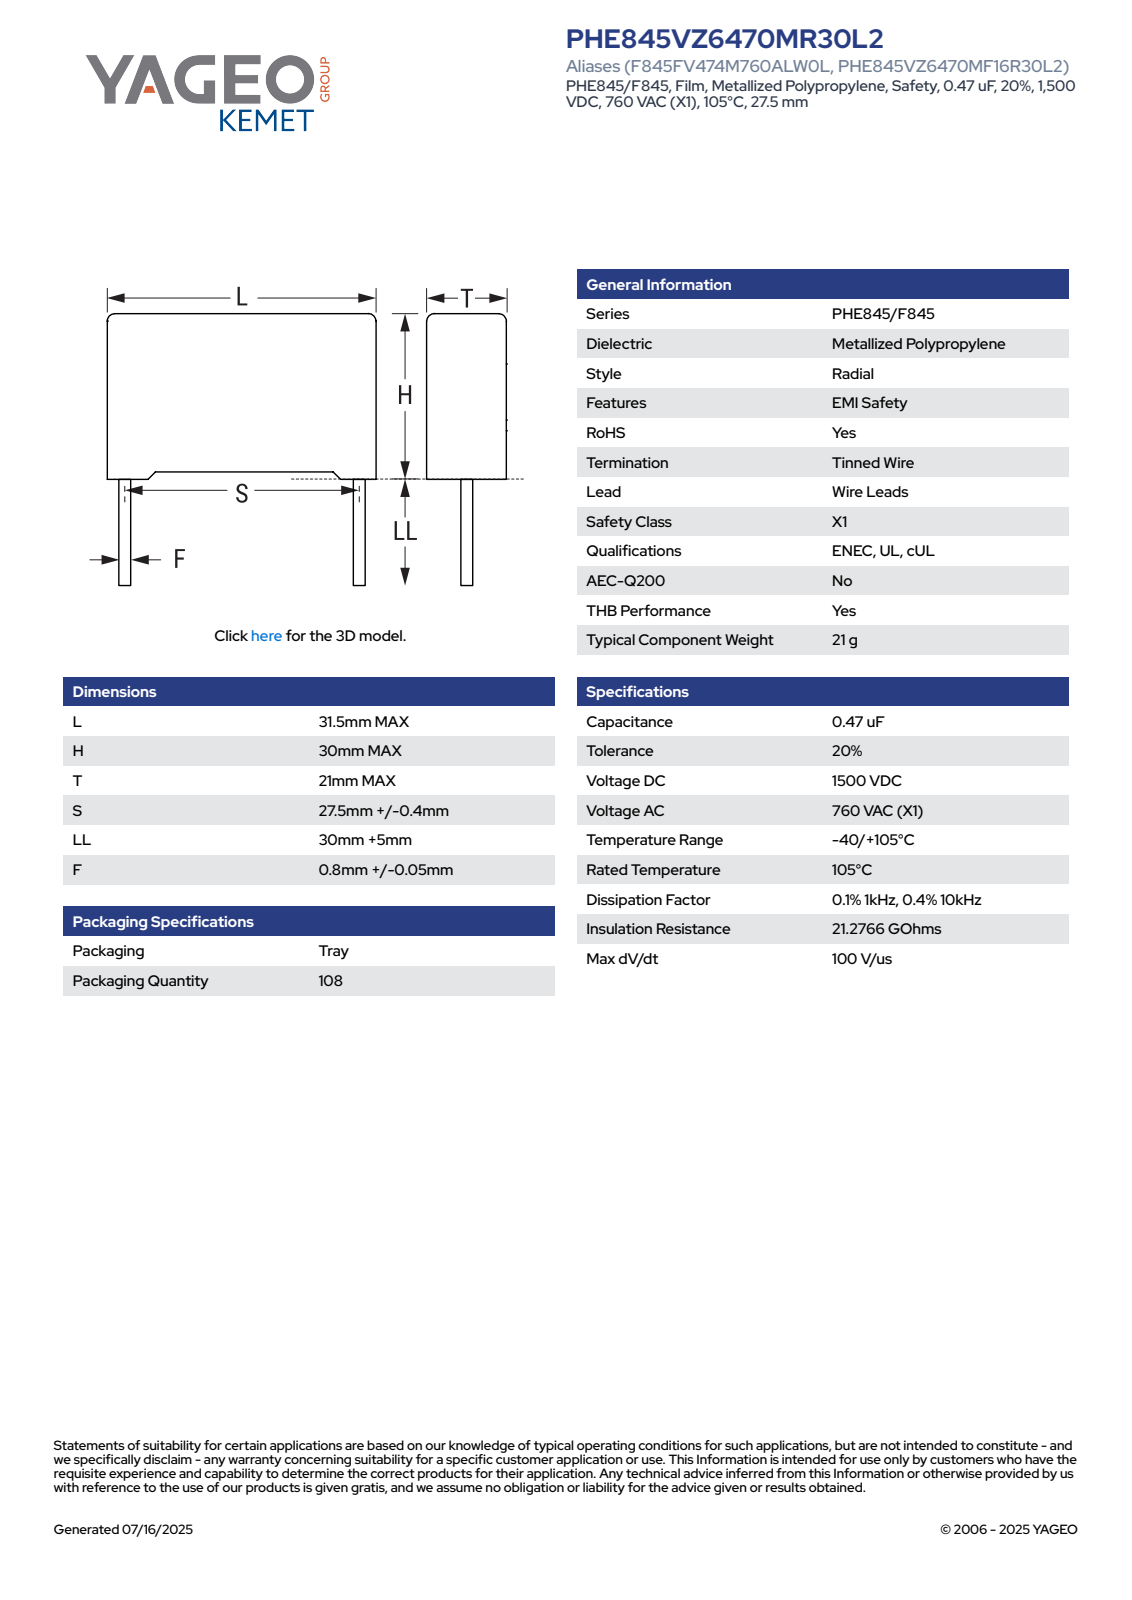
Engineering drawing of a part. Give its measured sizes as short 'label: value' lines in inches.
name: CFR_RB2_31.5X30X21_L31.5H30T21S27.5LL35F0.8
written by: SolidWorks 2021 (AUTOMOTIVE_DESIGN)
unit: in
bodies: 4 solids, 85 faces (77 planar, 8 cylindrical, 0 other)
size: 2.559 × 1.24 × 0.827
volume: 1.177 in³; area: 7.283 in²
bosses: 2× ⌀0.031
rounds: 4× R0.02
face distances: 0.827, 1.24, 1.141, 1.152, 0.03, 0.041, 1.181, 0.041, 1.199, 0.827
